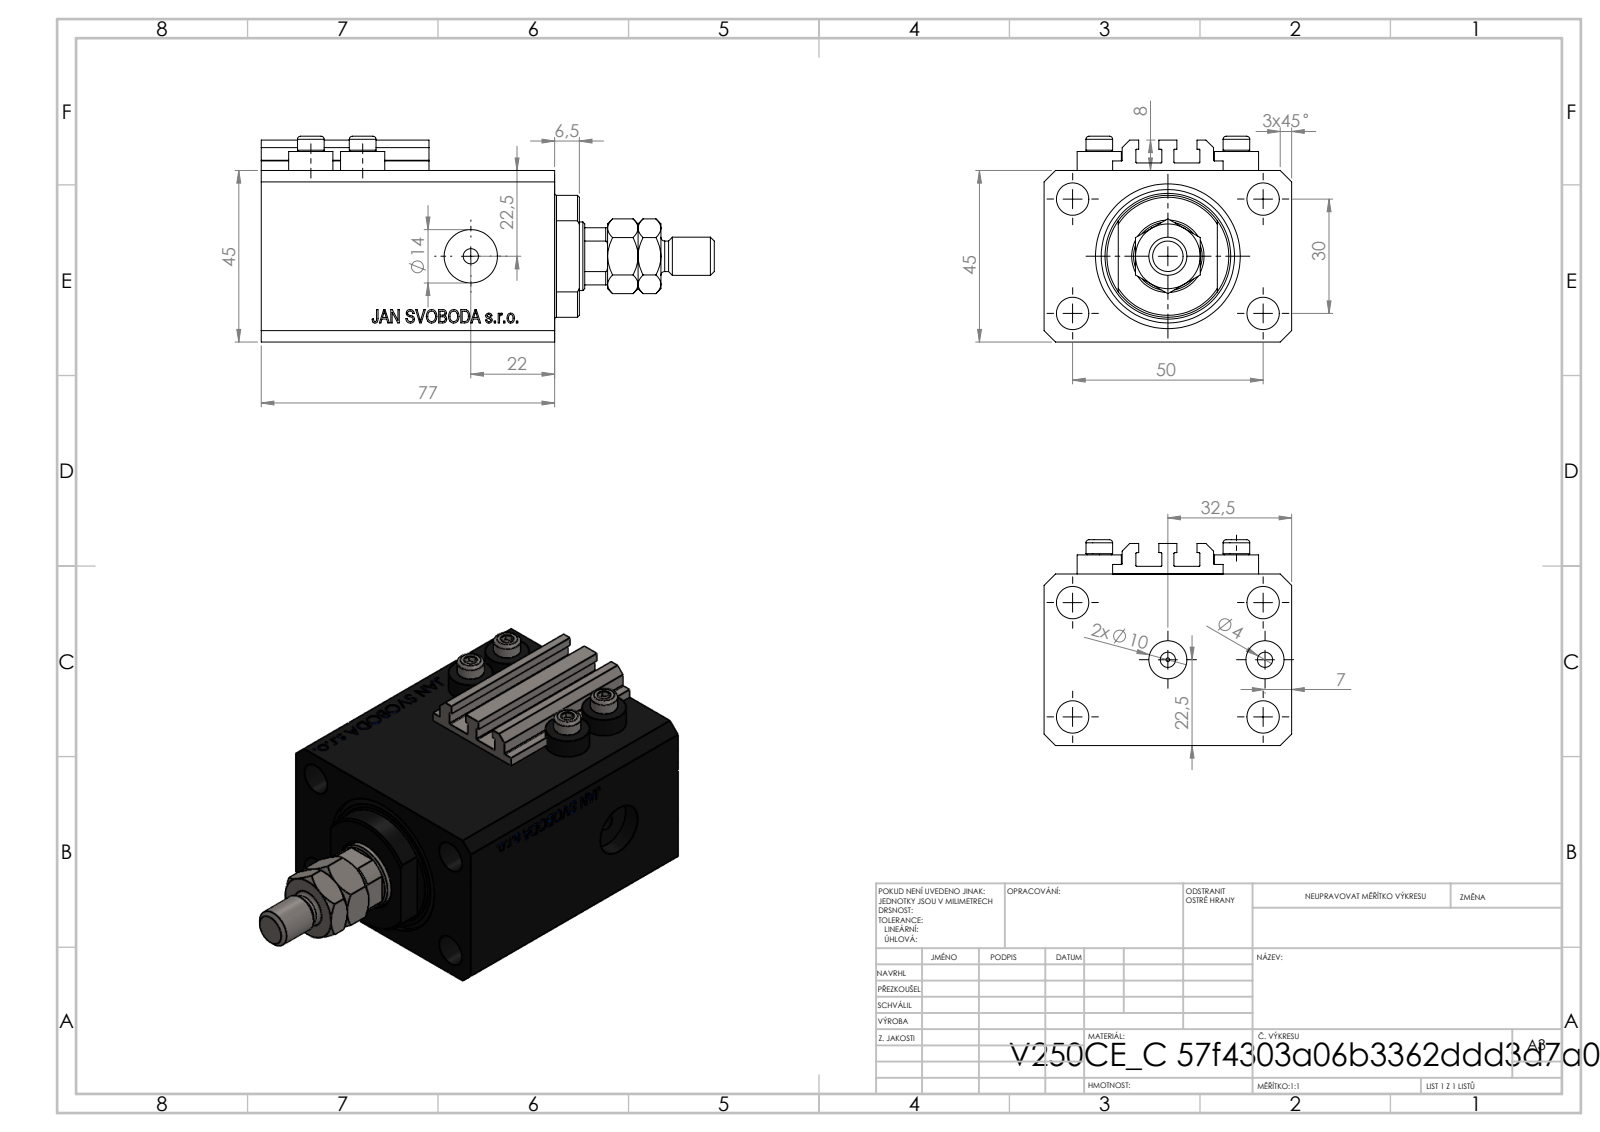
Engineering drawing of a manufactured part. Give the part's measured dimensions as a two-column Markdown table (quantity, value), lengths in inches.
| quantity | value |
| --- | --- |
| part name | ALLEN BOLT V250CE; V250CE_C_Body; V250CE_C_VCP; MTA (+1 more) |
| STEP written by | SolidWorks 2019 (CONFIG_CONTROL_DESIGN) |
| units | inches |
| bodies | 9 solids, 1091 faces (519 planar, 96 cylindrical, 476 other) |
| overall size | 4.685 × 2.559 × 2.126 |
| volume | 13.18 in³ |
| surface area | 92.1 in² |
| round holes (diameter × count) | 0.157 × 8, 0.335 × 5, 0.394 × 2, 0.551 × 2, 0.049 × 1, 0.709 × 1, 0.984 × 1, 1.496 × 1 |
| round bosses / shafts (diameter × count) | 0.457 × 4, 0.276 × 4, 0.315 × 1 |
| partial cylindrical surfaces (radius × count) | 0.008 × 10, 0.335 × 1, 0.63 × 1 |
| main face-to-face distances | 1.772, 2.559, 0.551, 3.031, 2.48, 0.272, 2.209, 2.76, 0.807, 0.118 |
| hole center spacings | 1.148, 0.535, 0.591, 1.181, 1.417, 1.515, 1.969, 2.074 |
